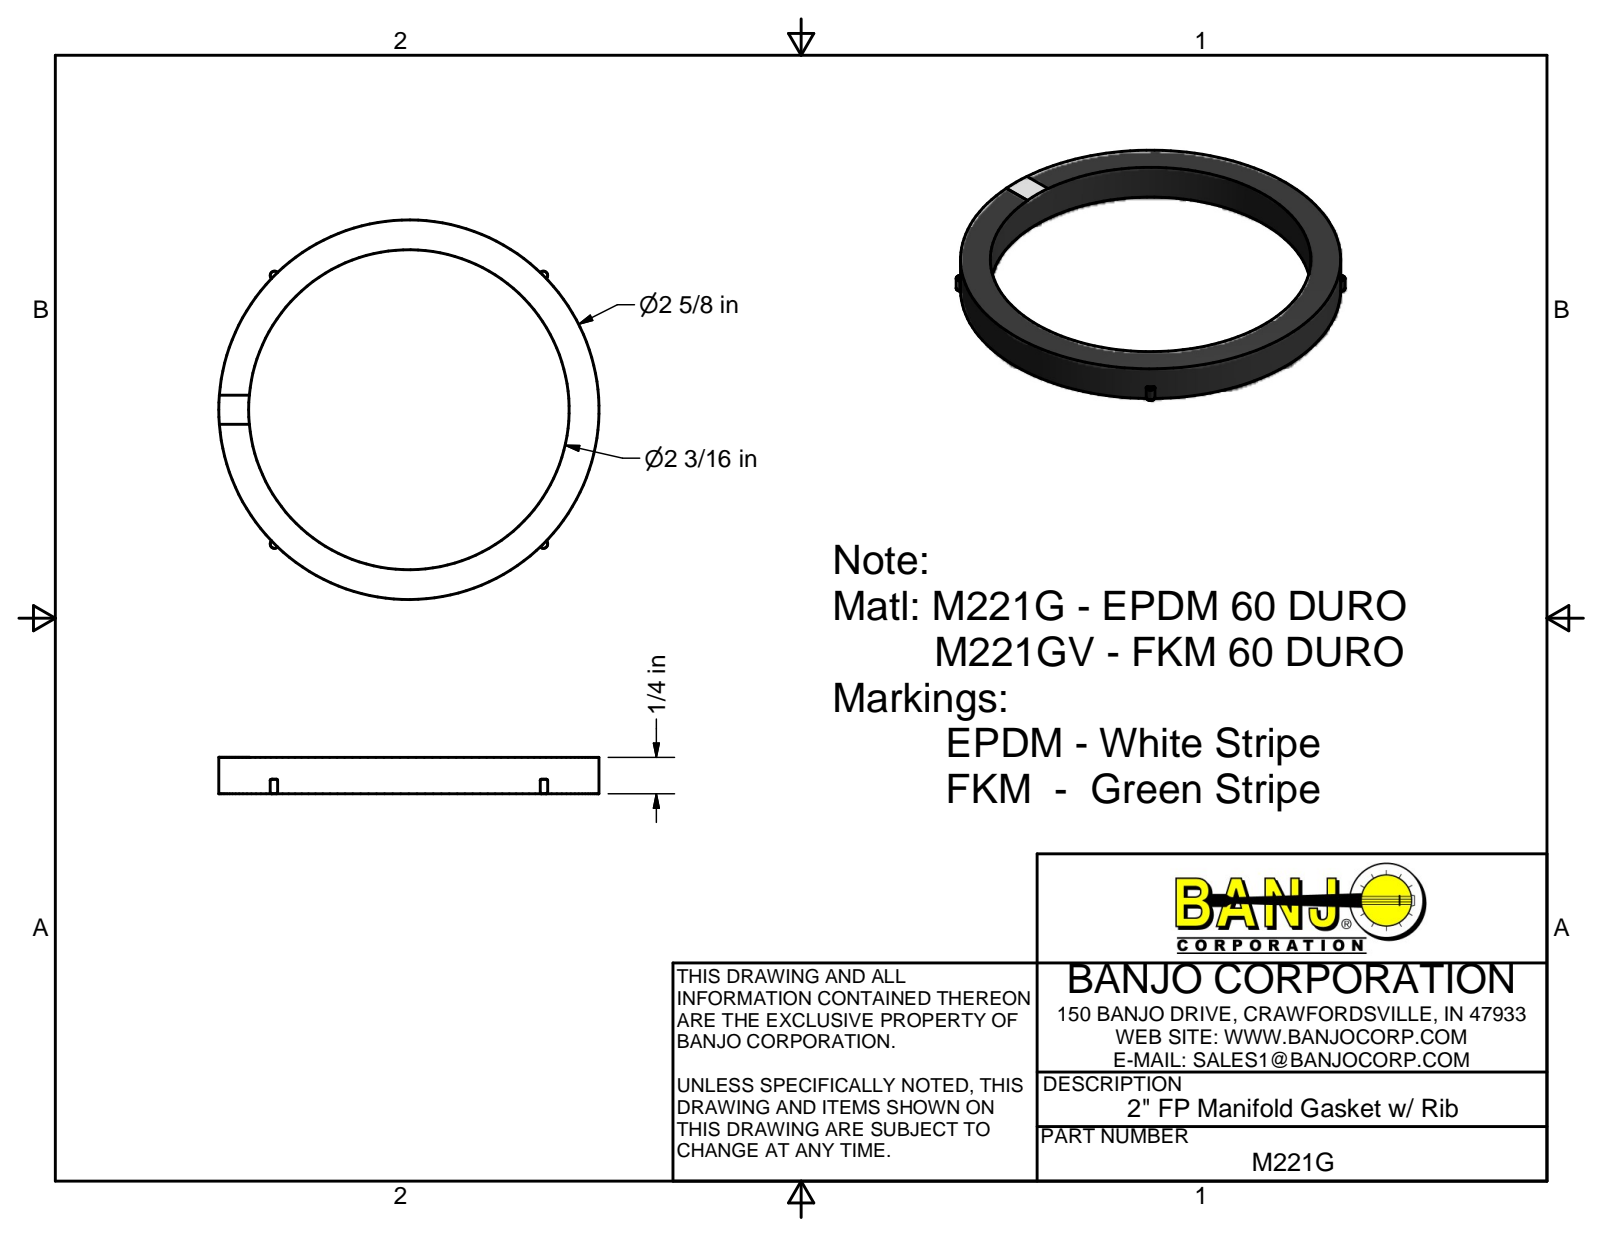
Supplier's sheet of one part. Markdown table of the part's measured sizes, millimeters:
| quantity | value |
| --- | --- |
| part name | M221G |
| STEP written by | Autodesk Inventor 2011 (AUTOMOTIVE_DESIGN) |
| units | millimeters |
| bodies | 1 solid, 23 faces (9 planar, 6 cylindrical, 8 other) |
| overall size | 66.3 × 66.3 × 6.4 |
| volume | 6 360 mm³ |
| surface area | 4 451 mm² |
| round holes (diameter × count) | 55.9 × 1 |
| round bosses / shafts (diameter × count) | 66.3 × 1 |
| partial cylindrical surfaces (radius × count) | 0.8 × 4 |
| main face-to-face distances | 6.4, 6.4, 3.8, 3.8, 2.5, 5.1 |
